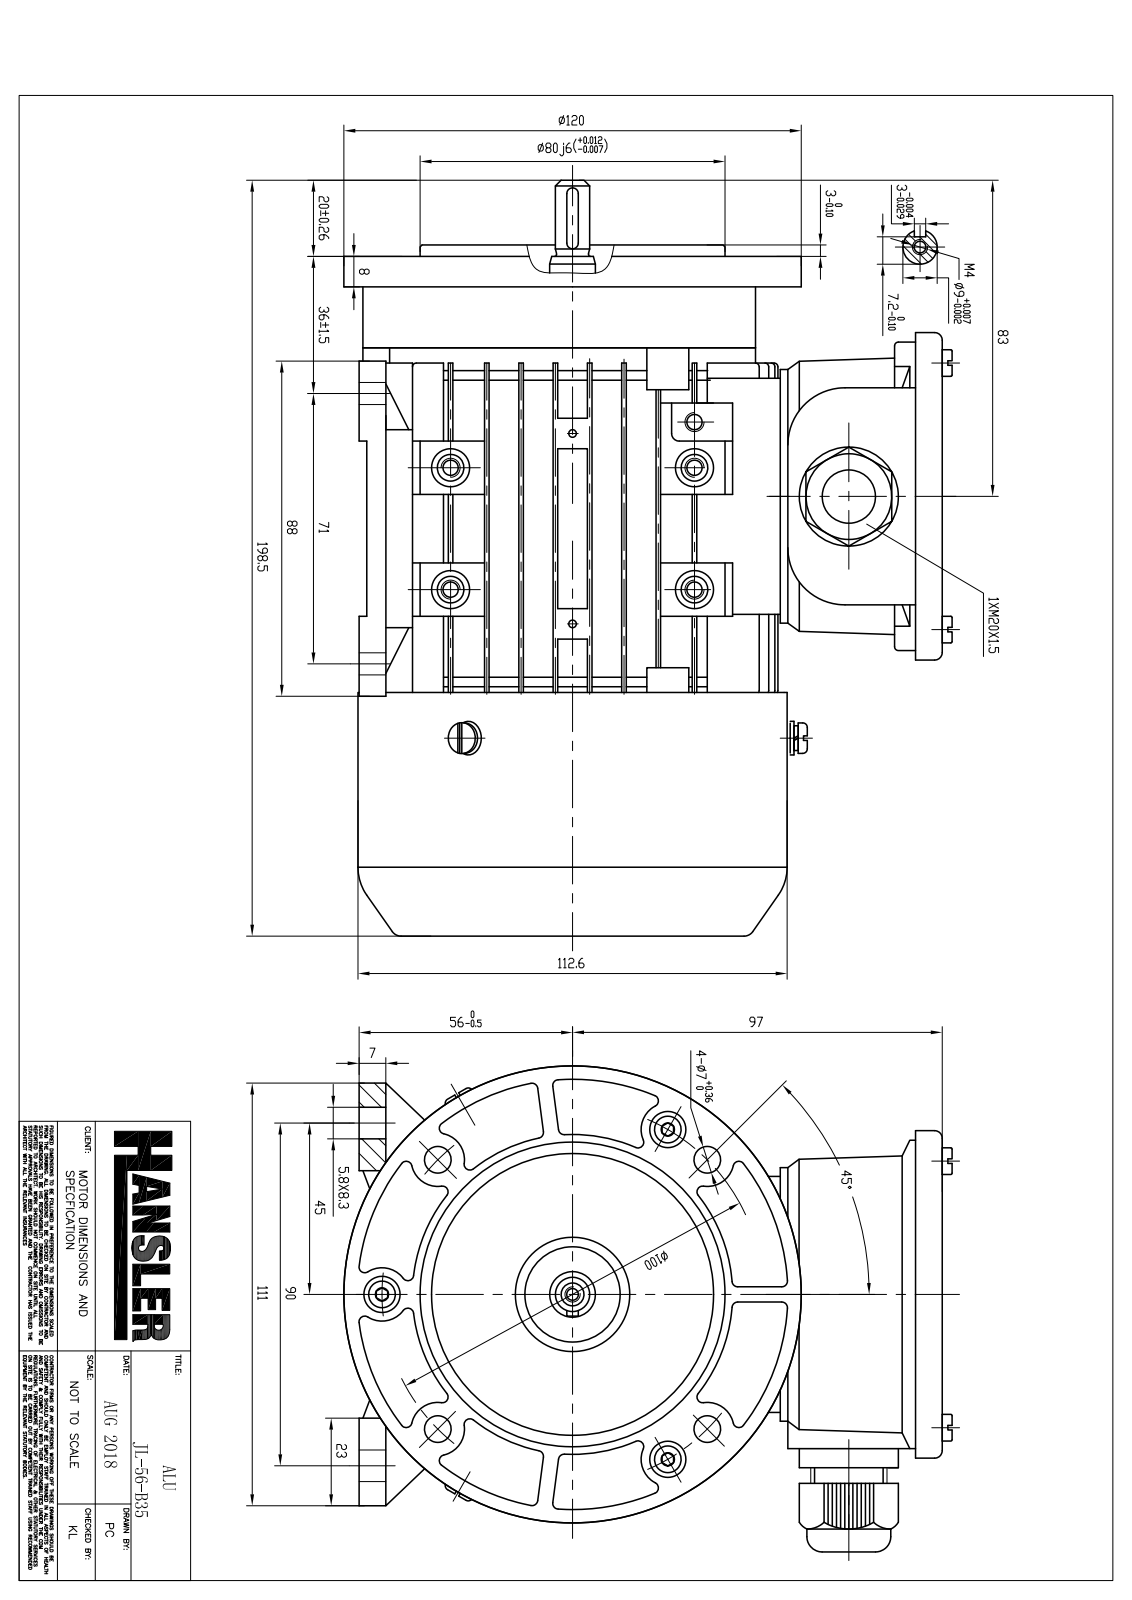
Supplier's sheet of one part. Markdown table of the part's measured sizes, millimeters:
| quantity | value |
| --- | --- |
| part name | JL-56-B35 |
| STEP written by | SIEMENS PLM Software NX 12.0 (AP203_CONFIGURATION_CONTROLLED_3D_DESIGN_OF_MECHANICAL_PARTS_AND_ASSEMBLIES_MIM_LF) |
| units | millimeters |
| bodies | 44 solids, 3247 faces (1812 planar, 1102 cylindrical, 333 other) |
| overall size | 198.42 × 158.4 × 123.58 |
| volume | 445 221 mm³ |
| surface area | 356 295 mm² |
| round holes (diameter × count) | 3 × 18, 4 × 13, 10 × 8, 4.7 × 7, 4.25 × 6, 4.13 × 4, 5 × 4, 5.25 × 4, 6 × 4, 7 × 4, 7.5 × 4, 2 × 3 |
| round bosses / shafts (diameter × count) | 7 × 11, 3.55 × 10, 4 × 9, 6.45 × 6, 9.5 × 4, 8.5 × 4, 7.85 × 4, 5 × 4 |
| partial cylindrical surfaces (radius × count) | 0.5 × 260, 1.5 × 48, 1 × 45, 2 × 39, 3 × 36, 5 × 16, 6 × 12, 2.9 × 8 |
| main face-to-face distances | 8.68, 2, 17.36, 26.04, 1.2, 34.72, 9.88, 7.48, 4, 27.24 |
| hole center spacings | 44, 58.46, 32, 50, 65.3, 12, 17.63, 18.38 |
